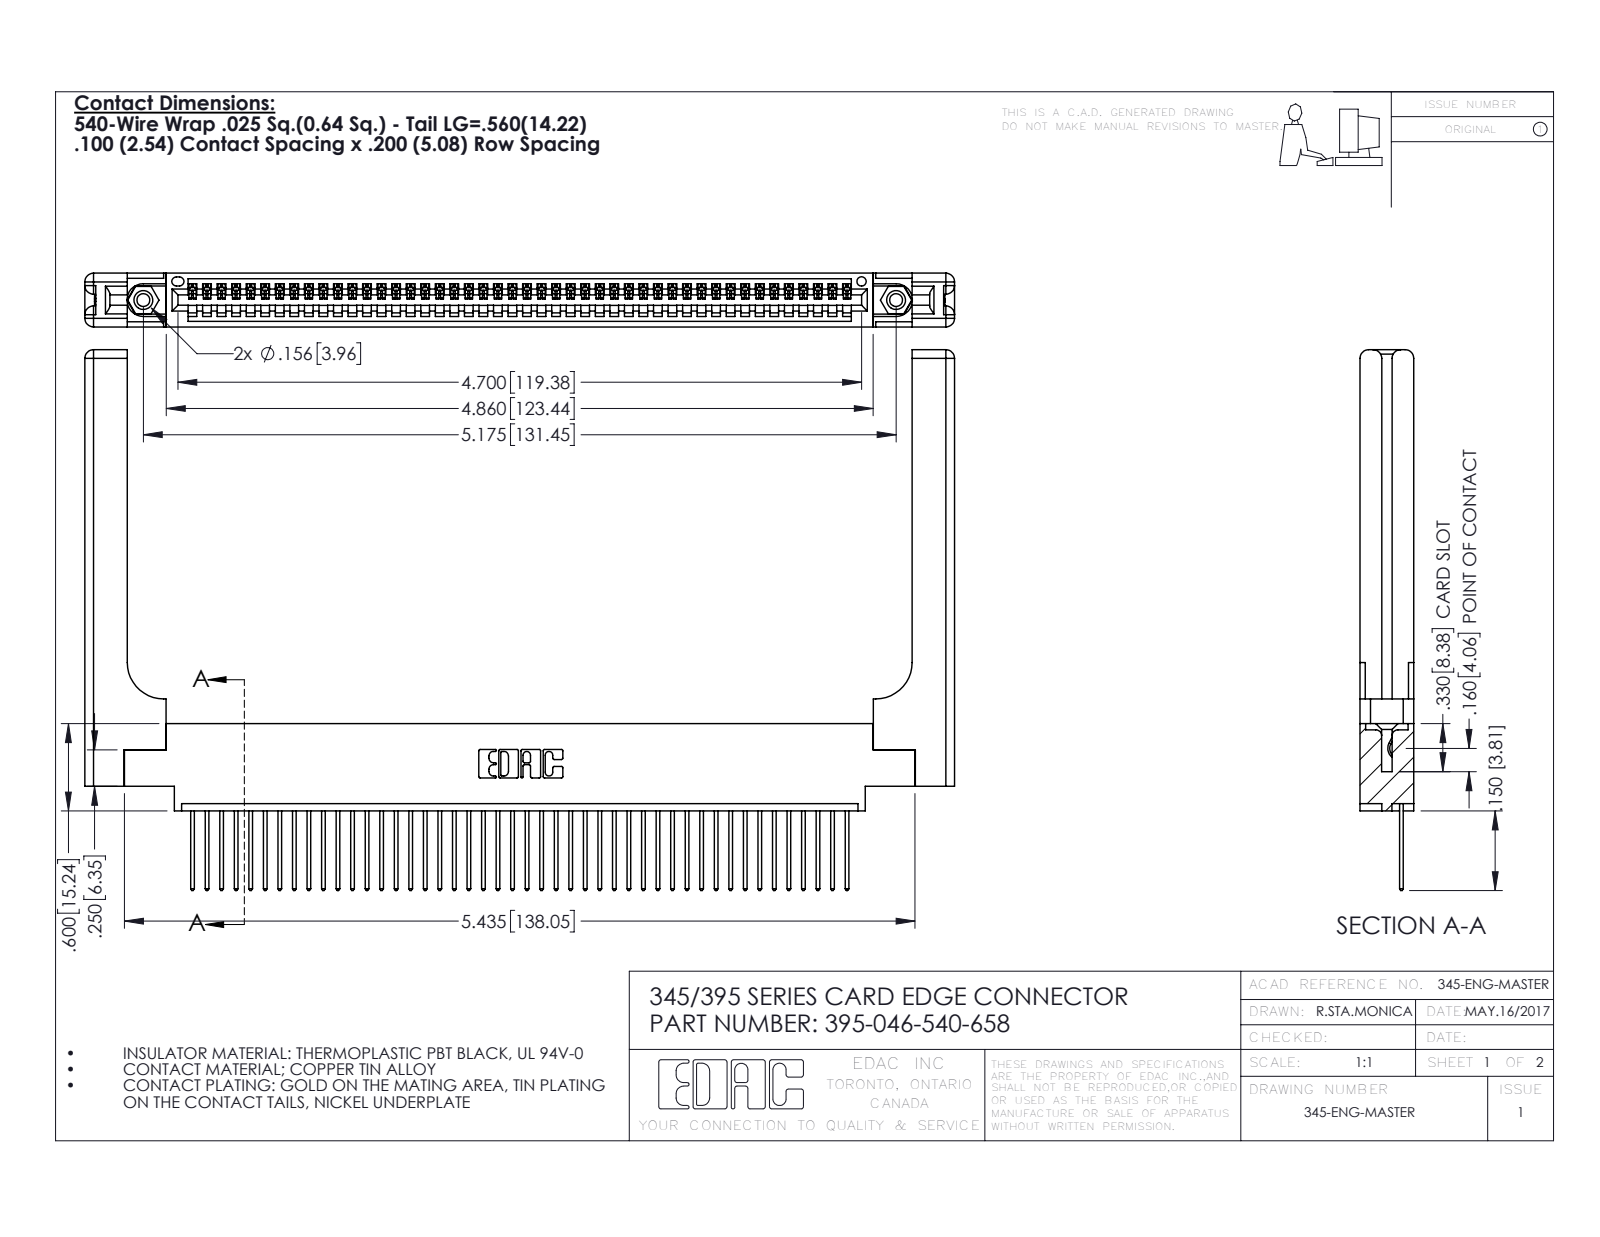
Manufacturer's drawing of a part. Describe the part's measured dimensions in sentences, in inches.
The part is named "345 Part_0.170 Offset - 0.156 Dia-TH; 345-292-001_345-293-140; 395-046-540-658; 345-250-001_345-250-001-102 (+1 more)". Its 3-D file was written by "SolidWorks 2016 (CONFIG_CONTROL_DESIGN)". It is 51 solids with 3054 faces: 2072 planar, 922 cylindrical and 60 other. Overall it measures 5.979 by 3.717 by 0.37 inches. Its volume is 1.398 cubic inches and its surface area 38.87 square inches. Round holes: 2 of diameter 0.089, 2 of diameter 0.125, 2 of diameter 0.156, 1 of diameter 0.064. Round bosses or shafts: 2 of diameter 0.155. Partial cylindrical surfaces (rounded edges, fillets, slot ends): 92 of radius 0.006, 92 of radius 0.01, 22 of radius 0.01, 16 of radius 0.06, 6 of radius 0.007, 6 of radius 0.031, 3 of radius 0.026, 2 of radius 0.03. The main face-to-face distances are 0.072, 0.37, 0.298, 0.098, 0.272, 0.025, 0.2, 0.225, 0.148, 0.15. The hole center spacings are 0.27, 4.939, 5.175.
